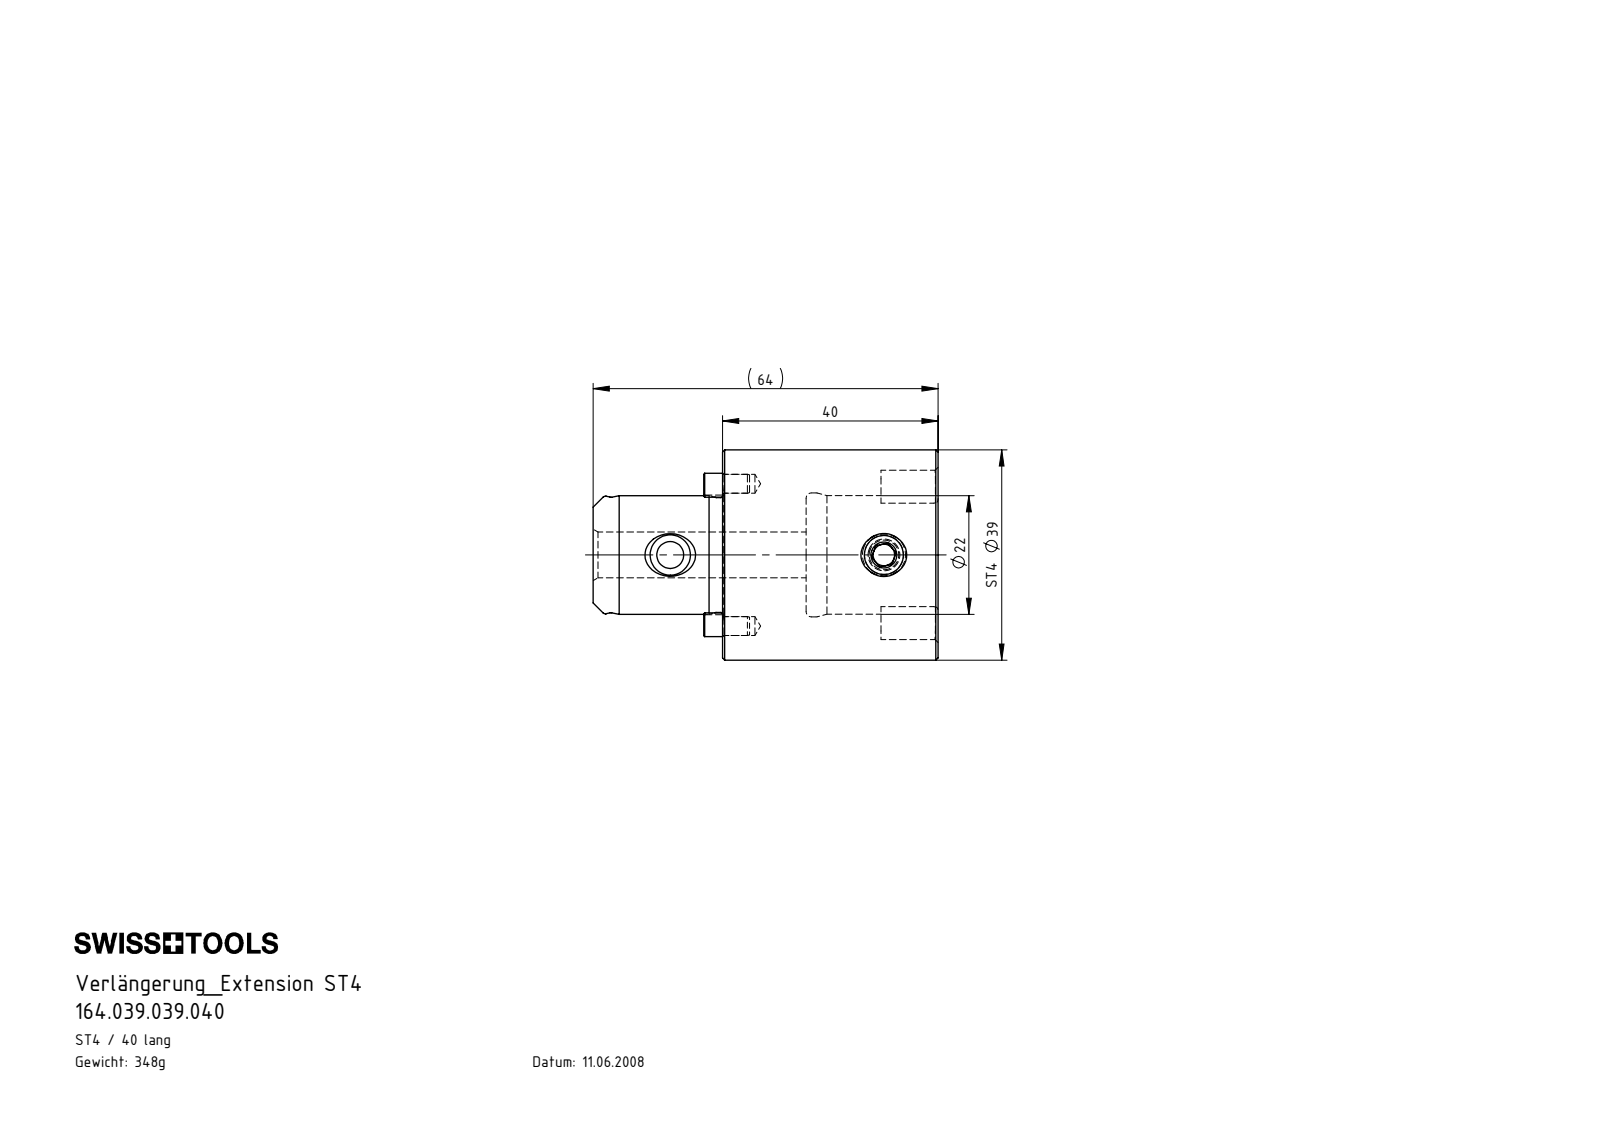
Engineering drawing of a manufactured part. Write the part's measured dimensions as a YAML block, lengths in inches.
part_name: "ST4-ER1.001.011_A; ST4-ST4.K01.040_A; ST4-ER2.001.009_A; ST4-ST4.K01.040"
step_written_by: "SolidWorks 2015 (CONFIG_CONTROL_DESIGN)"
units: inches
bodies: {solids: 4, faces: 150, planar: 26, cylindrical: 43, other: 81}
overall_size: [2.52, 1.535, 1.535]
volume: 2.704
surface_area: 19.51
round_holes:
  - {diameter: 0.138, count: 2}
  - {diameter: 0.197, count: 1}
  - {diameter: 0.285, count: 1}
  - {diameter: 0.335, count: 1}
  - {diameter: 0.866, count: 1}
  - {diameter: 0.906, count: 1}
round_bosses_or_shafts:
  - {diameter: 1.535, count: 1}
  - {diameter: 0.858, count: 1}
  - {diameter: 0.839, count: 1}
  - {diameter: 0.315, count: 1}
partial_cylinders:
  - {radius: 0.02, count: 4}
  - {radius: 0.126, count: 2}
  - {radius: 0.137, count: 2}
  - {radius: 0.435, count: 2}
face_to_face_distances: [1.575, 0.61, 0.965, 0.945, 1.555, 2.52, 0.744, 2.102, 1.157, 0.547]
hole_center_spacings: [0.52, 1.039, 1.561]
